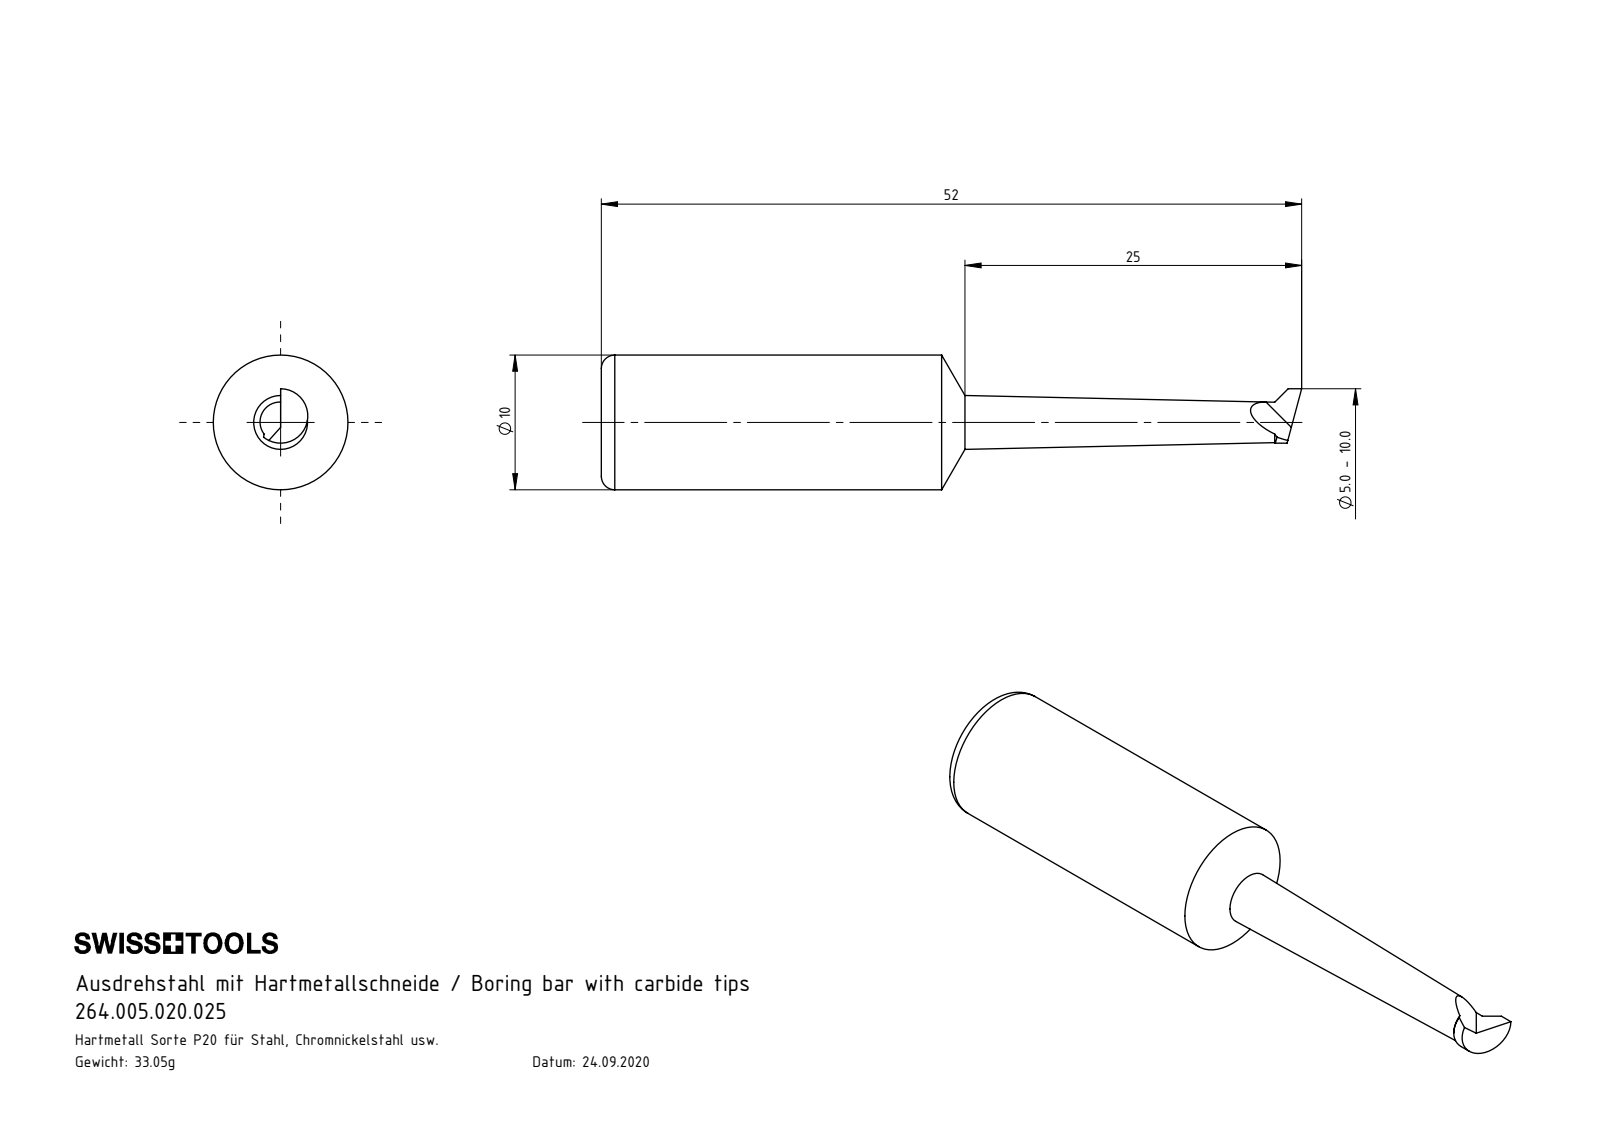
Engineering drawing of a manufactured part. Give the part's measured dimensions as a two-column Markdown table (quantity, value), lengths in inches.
| quantity | value |
| --- | --- |
| part name | U10.B05.002.025 |
| STEP written by | SolidWorks 2017 (AUTOMOTIVE_DESIGN) |
| units | inches |
| bodies | 1 solid, 10 faces (4 planar, 2 cylindrical, 4 other) |
| overall size | 2.047 × 0.394 × 0.394 |
| volume | 0.139 in³ |
| surface area | 1.879 in² |
| round bosses / shafts (diameter × count) | 0.394 × 1 |
| partial cylindrical surfaces (radius × count) | 0.08 × 1 |
